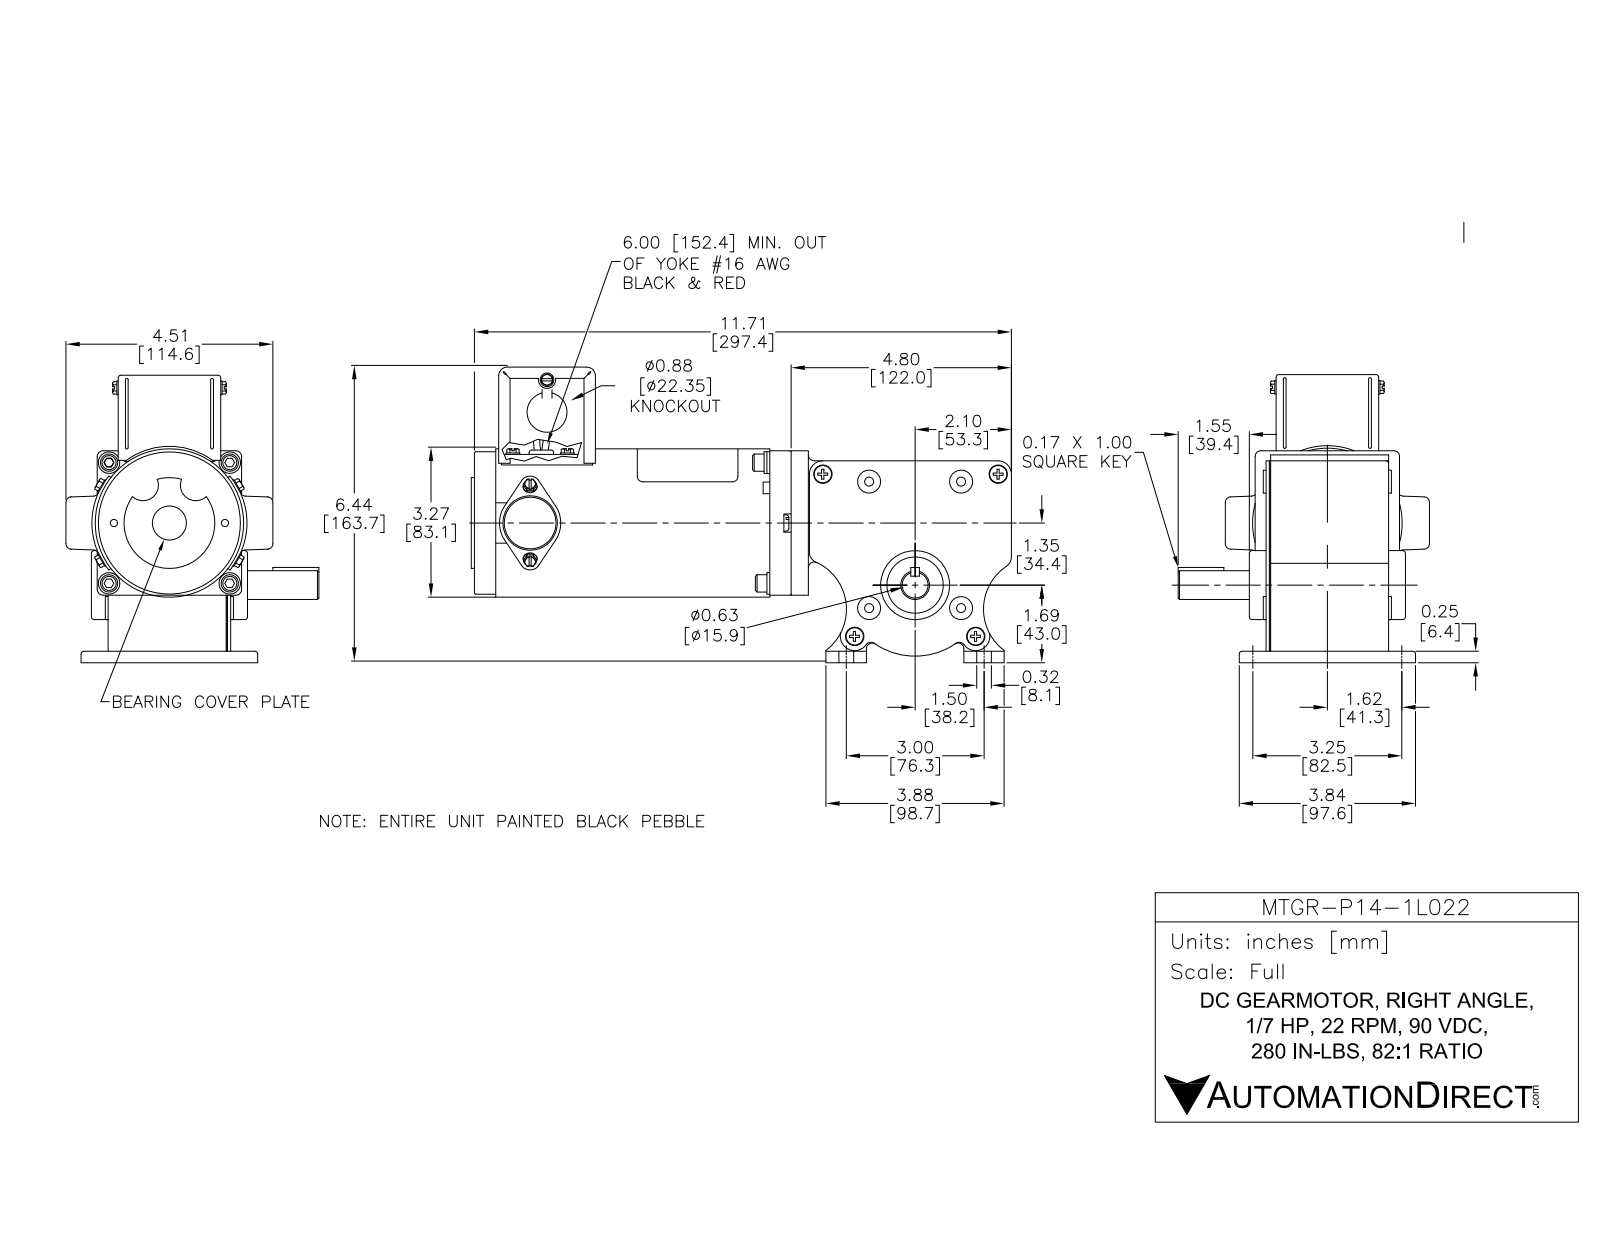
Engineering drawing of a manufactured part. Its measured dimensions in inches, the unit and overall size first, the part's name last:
Units: inches
Overall size (bounding box): 11.791 × 6.522 × 5.415
Round holes (diameter × count): ⌀0.5 ×5, ⌀0.125 ×4, ⌀0.197 ×4, ⌀0.4 ×4, ⌀0.198 ×2, ⌀0.25 ×1, ⌀0.3 ×1, ⌀0.375 ×1, ⌀0.625 ×1, ⌀1 ×1, ⌀1.125 ×1, ⌀1.5 ×1
Round bosses / shafts (diameter × count): ⌀0.375 ×6, ⌀0.3 ×4, ⌀0.375 ×3, ⌀0.125 ×2, ⌀0.1 ×2, ⌀3.156 ×1, ⌀0.625 ×1, ⌀0.301 ×1
Partial cylindrical surfaces — rounded edges, fillets, slot ends (radius × count): R0.125 ×4, R0.16 ×4, R0.191 ×4, R0.234 ×4, R0.25 ×4, R0.13 ×2, R0.159 ×2, R0.29 ×2
Main face-to-face distances: 0.015, 0.03, 0.031, 2.603, 2.588, 2.573, 0.1, 0.07, 0.085, 2.673
Hole centre spacings: 1.318, 1.859, 2.63, 2.865, 1.118, 1.23, 2, 2.37
Volume: 64.64 in³ · Surface area: 475.7 in²
Bodies: 43 solids, 797 faces (486 planar, 283 cylindrical, 28 other)
Part name (STEP PRODUCT): P14-1L022
STEP written by: SolidWorks 2013 (AUTOMOTIVE_DESIGN)
